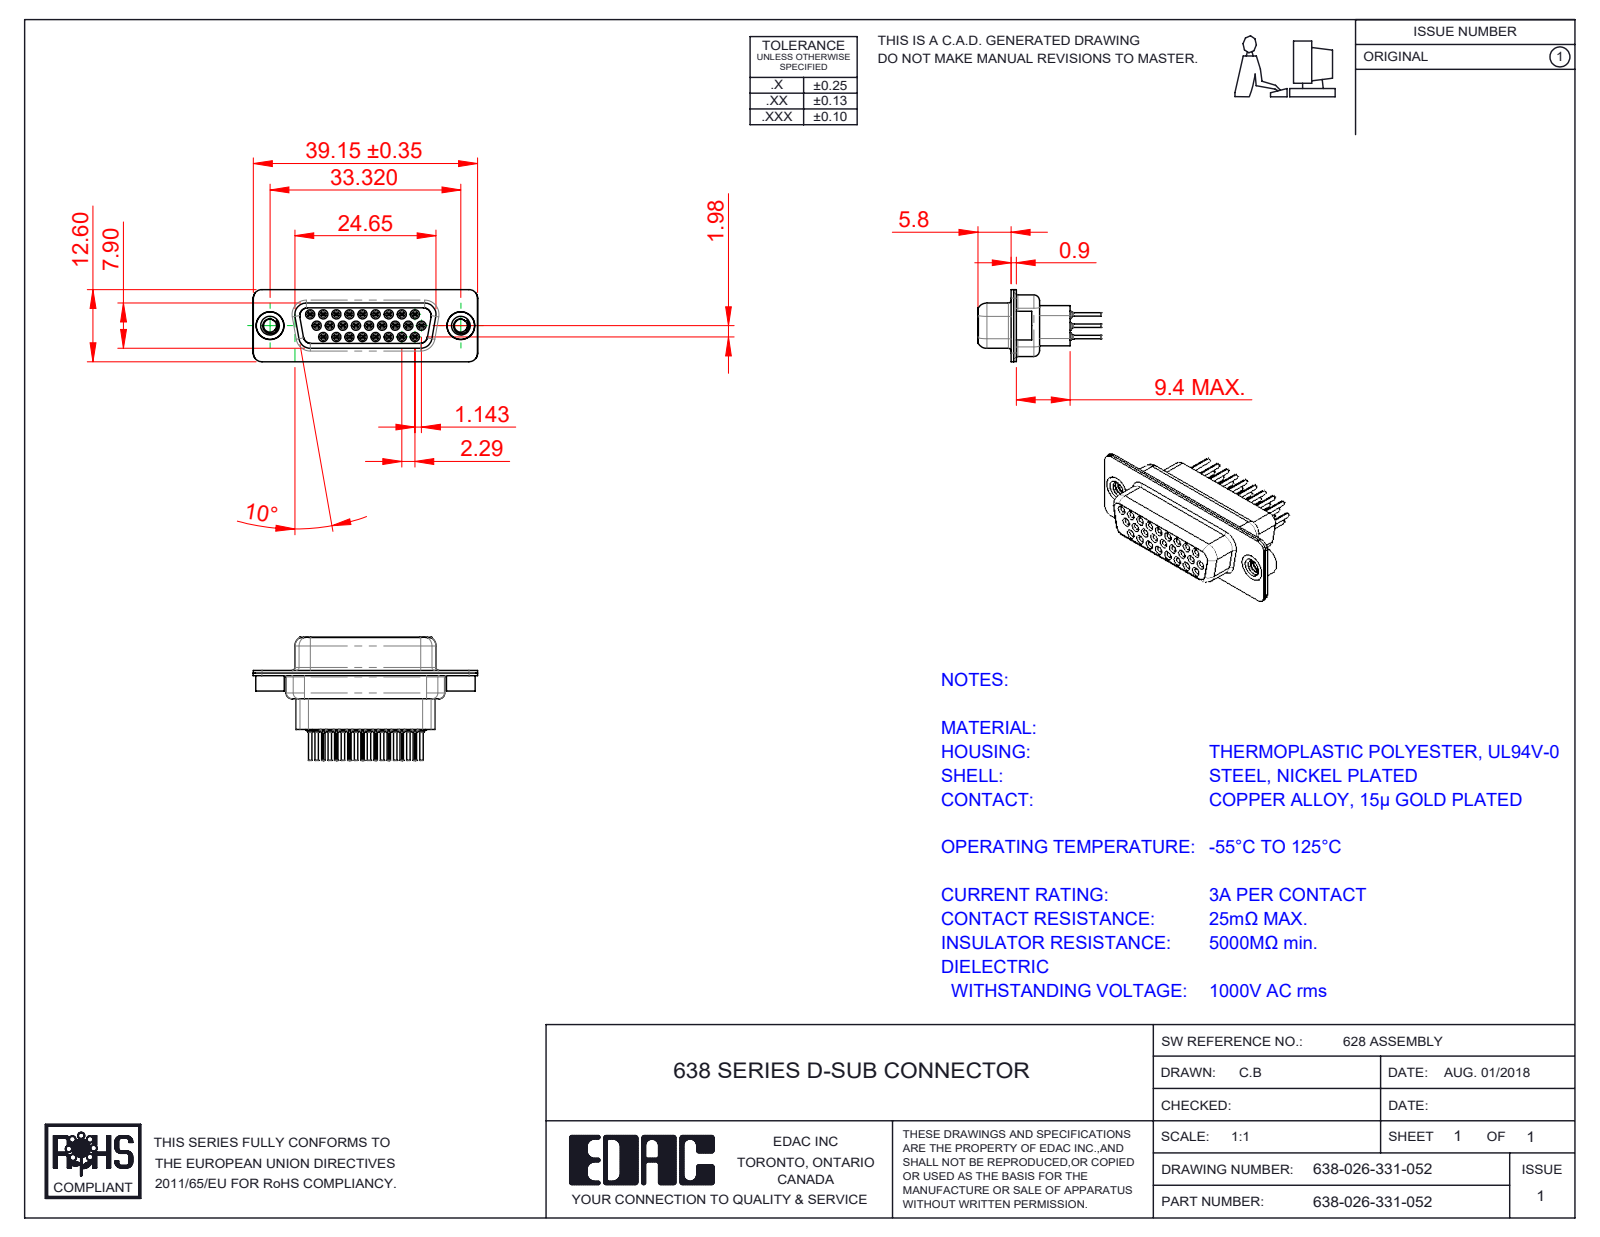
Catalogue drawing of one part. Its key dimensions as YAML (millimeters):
part_name: "638 Shell Rear_26 Contacts; 638 Shell Front_26 Contacts; 638 Contact Row 2_31; 638 Contact Row 3_31 (+4 more)"
step_written_by: "SolidWorks 2020 (CONFIG_CONTROL_DESIGN)"
units: millimeters
bodies: {solids: 31, faces: 3477, planar: 873, cylindrical: 995, other: 1609}
overall_size: [39.19, 21.5, 12.6]
volume: 2677
surface_area: 9873
round_holes:
  - {diameter: 0.2, count: 26}
  - {diameter: 0.8, count: 26}
  - {diameter: 1, count: 26}
  - {diameter: 1.1, count: 26}
  - {diameter: 1.6, count: 26}
  - {diameter: 1.7, count: 26}
  - {diameter: 1.8, count: 26}
  - {diameter: 2.26, count: 2}
  - {diameter: 4, count: 2}
  - {diameter: 4.05, count: 2}
  - {diameter: 4.85, count: 2}
round_bosses_or_shafts:
  - {diameter: 2, count: 26}
  - {diameter: 1.5, count: 26}
  - {diameter: 1.2, count: 26}
  - {diameter: 0.6, count: 26}
  - {diameter: 5, count: 2}
  - {diameter: 4.95, count: 2}
  - {diameter: 4.8, count: 2}
partial_cylinders:
  - {radius: 0.1, count: 52}
  - {radius: 1.5, count: 20}
  - {radius: 0.28, count: 18}
  - {radius: 2, count: 12}
  - {radius: 1.55, count: 8}
  - {radius: 1.35, count: 5}
  - {radius: 0.25, count: 4}
  - {radius: 0.5, count: 4}
face_to_face_distances: [0.45, 0.4, 6.6, 0.9, 1.43, 8.88, 7, 2.28, 9.4, 5.8]
hole_center_spacings: [3.96, 2.28, 4.57, 6.05, 2.29, 8.24, 6.86, 10.48]
